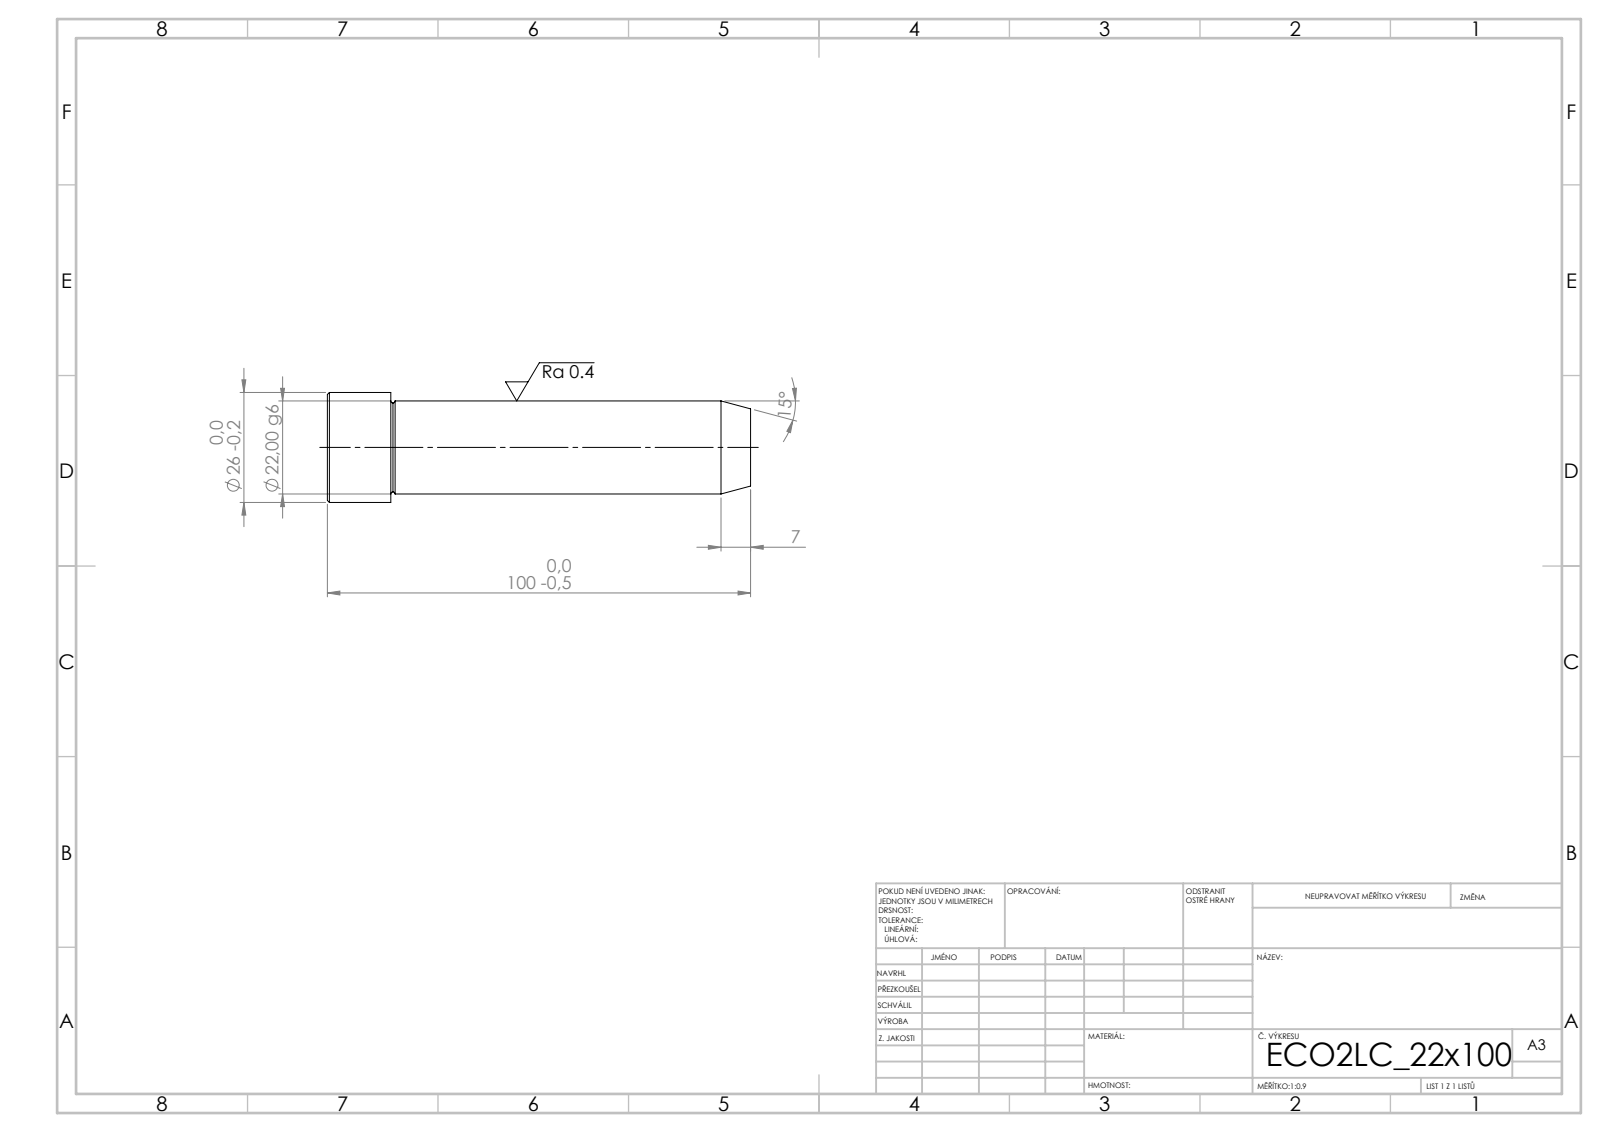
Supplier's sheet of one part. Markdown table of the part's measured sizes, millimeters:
| quantity | value |
| --- | --- |
| STEP written by | SolidWorks 2019 (CONFIG_CONTROL_DESIGN) |
| units | millimeters |
| bodies | 1 solid, 15 faces (3 planar, 4 cylindrical, 8 other) |
| overall size | 100 × 26 × 26 |
| volume | 39 811 mm³ |
| surface area | 8 030 mm² |
| round bosses / shafts (diameter × count) | 26 × 1, 22 × 1 |
| main face-to-face distances | 100, 85, 15 |
